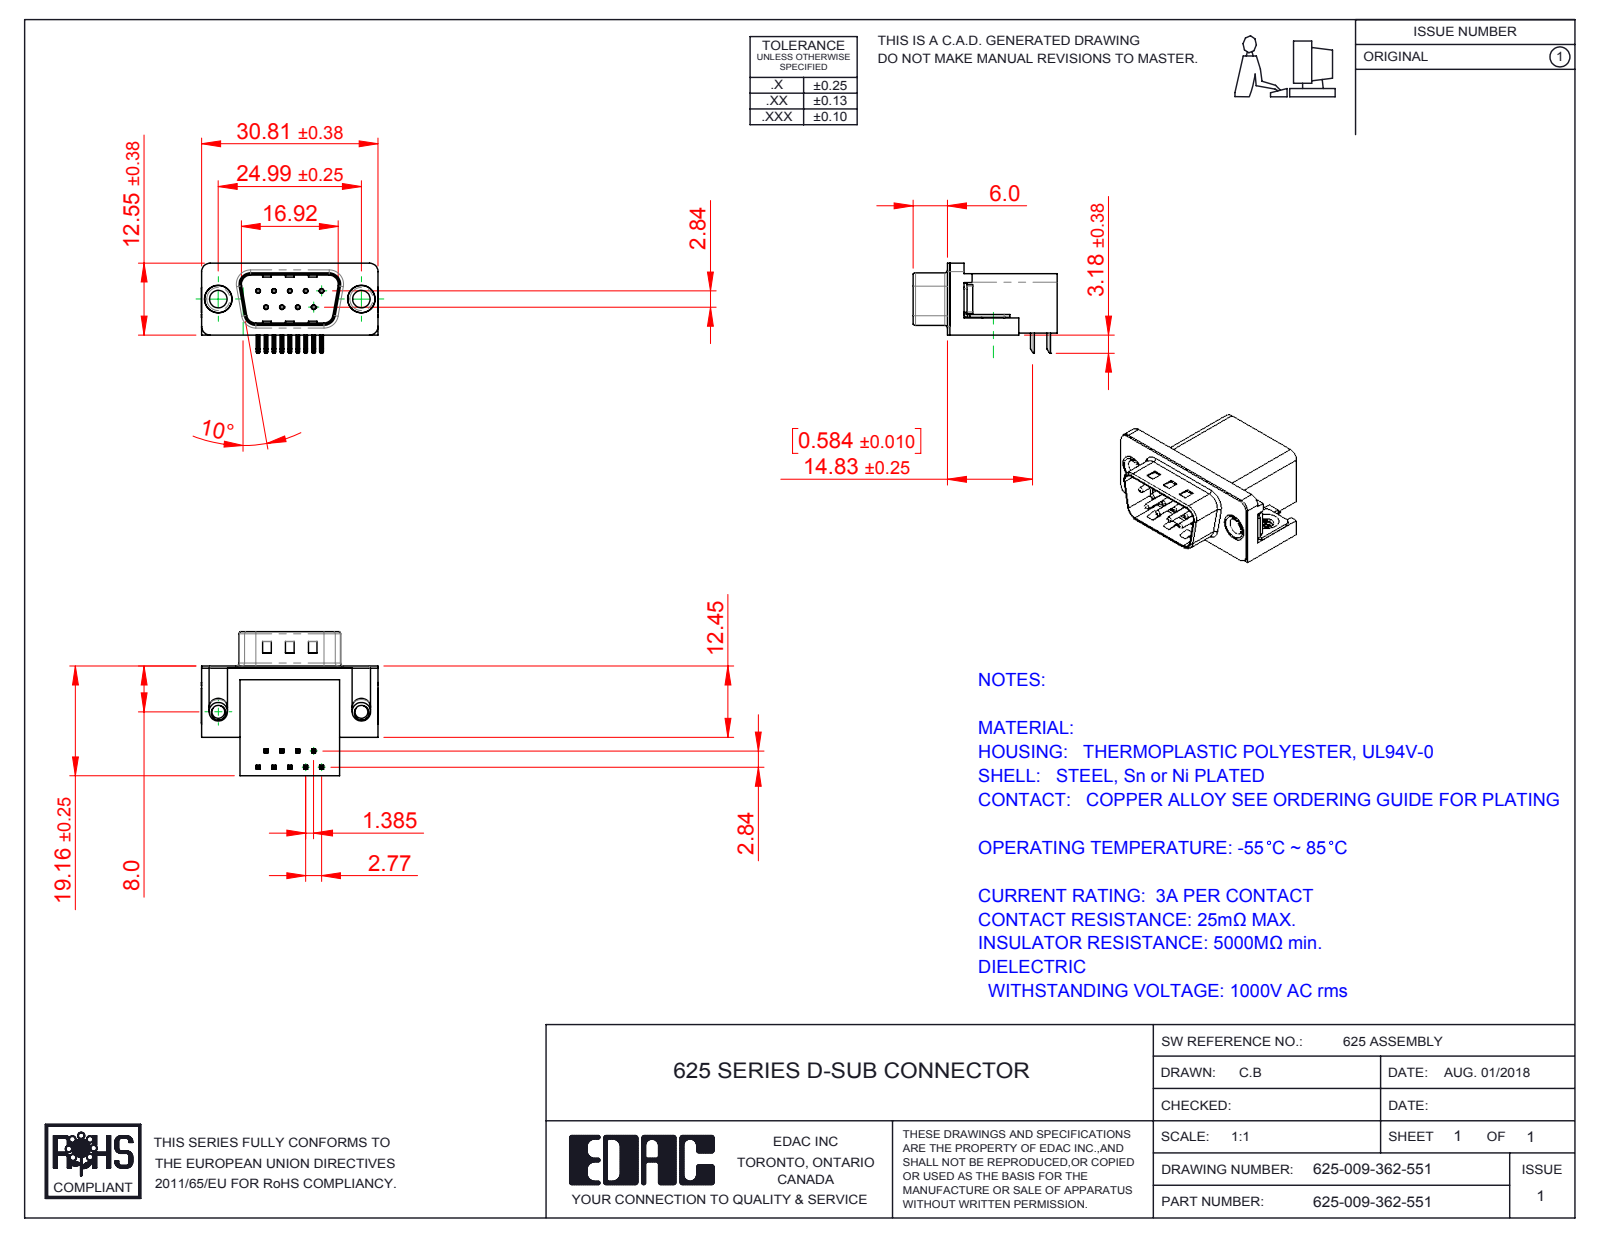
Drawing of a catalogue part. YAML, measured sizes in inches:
part_name: "625 Contact Bottom; 625 Shell_9 Socket; 625 4-40 Threaded Board Mount; 625 Housing_9 Socket (+3 more)"
step_written_by: "SolidWorks 2016 (CONFIG_CONTROL_DESIGN)"
units: inches
bodies: {solids: 15, faces: 985, planar: 575, cylindrical: 311, other: 99}
overall_size: [1.216, 0.991, 0.619]
volume: 0.273
surface_area: 7.761
round_holes:
  - {diameter: 0.014, count: 9}
  - {diameter: 0.031, count: 9}
  - {diameter: 0.089, count: 2}
  - {diameter: 0.12, count: 2}
  - {diameter: 0.157, count: 2}
  - {diameter: 0.189, count: 2}
  - {diameter: 0.197, count: 2}
round_bosses_or_shafts:
  - {diameter: 0.03, count: 9}
  - {diameter: 0.193, count: 2}
  - {diameter: 0.187, count: 2}
  - {diameter: 0.152, count: 2}
  - {diameter: 0.128, count: 2}
partial_cylinders:
  - {radius: 0.01, count: 44}
  - {radius: 0.005, count: 18}
  - {radius: 0.039, count: 16}
  - {radius: 0.02, count: 9}
  - {radius: 0.059, count: 8}
  - {radius: 0.063, count: 8}
  - {radius: 0.035, count: 4}
  - {radius: 0.079, count: 4}
face_to_face_distances: [0.016, 0.407, 0.739, 0.754, 0.114, 0.64, 0.098, 0.014, 0.421, 0.264]
hole_center_spacings: [0.124, 0.109, 0.218, 0.198, 0.198, 0.327, 0.294, 0.295]
